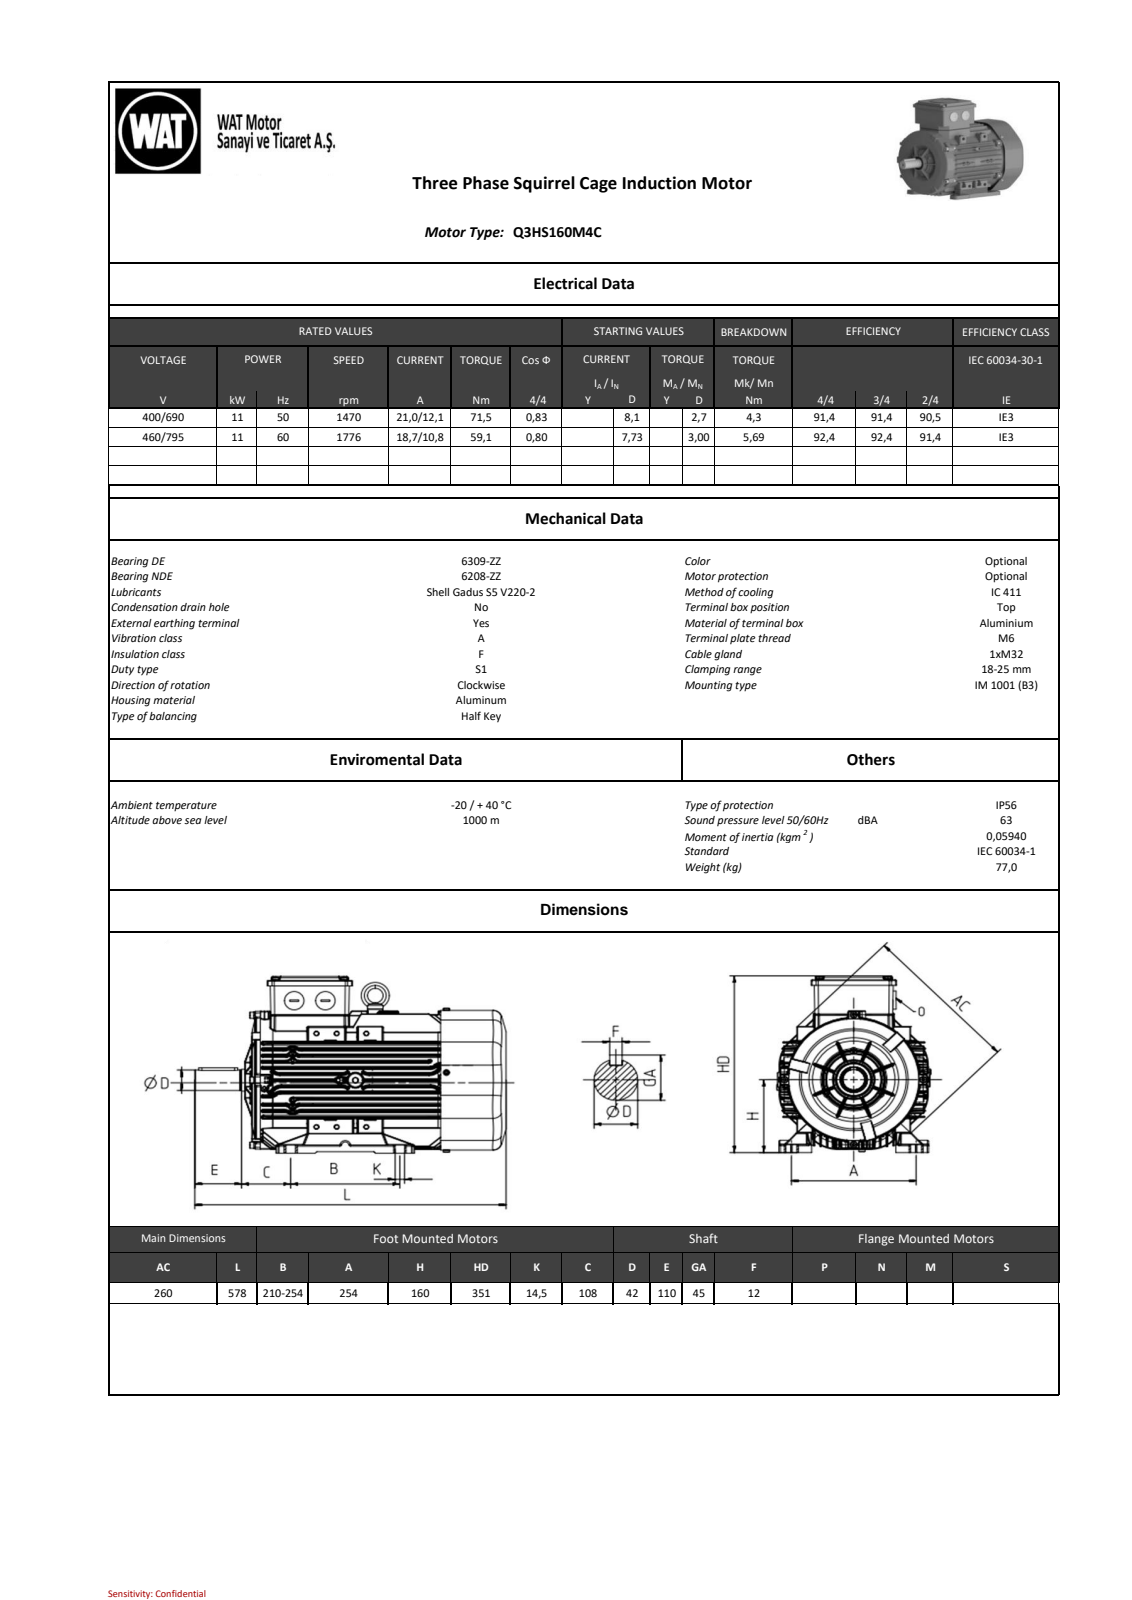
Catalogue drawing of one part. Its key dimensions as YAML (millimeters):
part_name: "QHS series_ 160_B3 _DEEP COVER__stp_objects"
step_written_by: "SIEMENS PLM Software NX2206.8101 (AP203_CONFIGURATION_CONTROLLED_3D_DESIGN_OF_MECHANICAL_PARTS_AND_ASSEMBLIES_MIM_LF)"
units: millimeters
bodies: {solids: 0, faces: 8742, planar: 2086, cylindrical: 3676, other: 2980}
overall_size: [578, 351.2, 287.5]
round_holes:
  - {diameter: 4.6, count: 3}
  - {diameter: 8.48, count: 2}
  - {diameter: 8.48, count: 1}
  - {diameter: 16, count: 1}
  - {diameter: 17, count: 1}
  - {diameter: 62, count: 1}
  - {diameter: 68.67, count: 1}
  - {diameter: 82, count: 1}
  - {diameter: 180, count: 1}
round_bosses_or_shafts:
  - {diameter: 13, count: 5}
  - {diameter: 8, count: 4}
  - {diameter: 38, count: 2}
  - {diameter: 230.5, count: 1}
  - {diameter: 86.77, count: 1}
  - {diameter: 45, count: 1}
  - {diameter: 42, count: 1}
  - {diameter: 41.4, count: 1}
partial_cylinders:
  - {radius: 1, count: 1013}
  - {radius: 0.8, count: 947}
  - {radius: 2, count: 265}
  - {radius: 3, count: 82}
  - {radius: 0.5, count: 46}
  - {radius: 1.5, count: 37}
  - {radius: 5, count: 31}
  - {radius: 60, count: 16}
face_to_face_distances: [10.42, 1.5, 10.56, 4, 10.28, 20.84, 125.58, 94.46, 21.12, 104.9]
hole_center_spacings: [31.88, 143, 178.91, 217.51]
